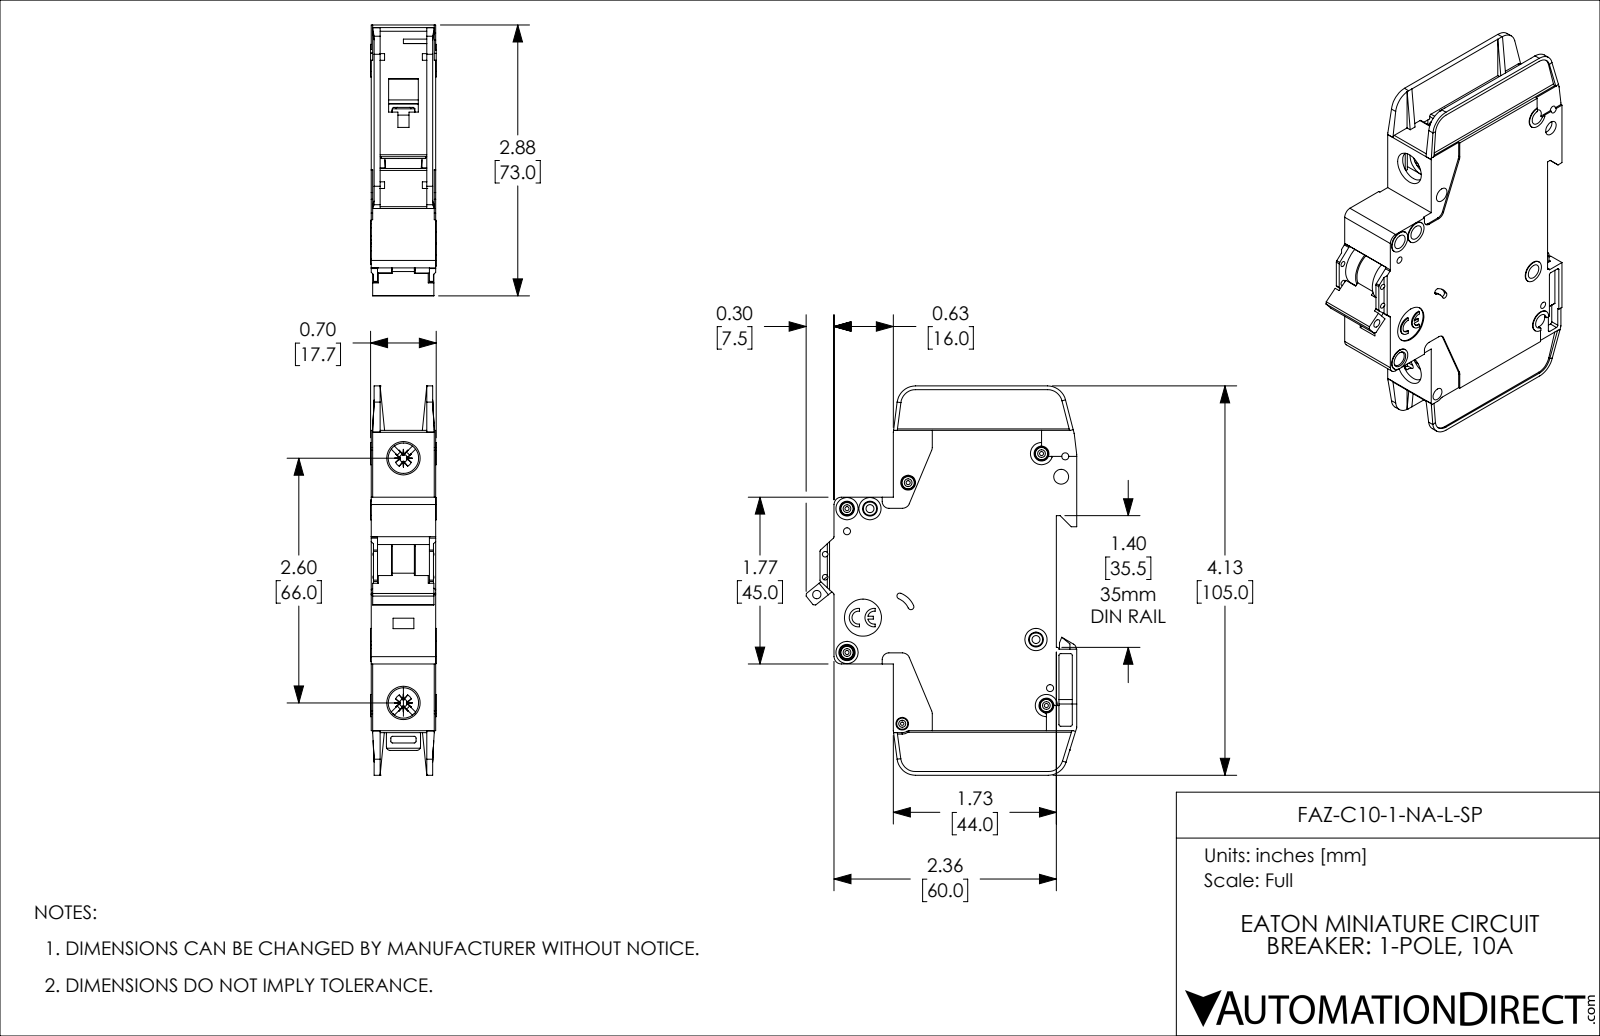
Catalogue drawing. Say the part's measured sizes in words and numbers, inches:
The part is named "FAZ-C10-1-NA-L-SP". Its 3-D file was written by "SolidWorks 2019 (AUTOMOTIVE_DESIGN)". It is 1 solid with 1127 faces: 671 planar, 357 cylindrical and 99 other. Overall it measures 4.134 by 2.876 by 0.697 inches. Its volume is 4.682 cubic inches and its surface area 41.01 square inches. Round holes: 8 of diameter 0.157, 5 of diameter 0.043, 4 of diameter 0.075, 2 of diameter 0.059, 2 of diameter 0.085, 2 of diameter 0.323, 1 of diameter 0.035, 1 of diameter 0.089, 1 of diameter 0.098, 1 of diameter 0.134, 1 of diameter 0.394. Round bosses or shafts: 5 of diameter 0.13, 4 of diameter 0.236, 2 of diameter 0.118, 1 of diameter 0.098. Partial cylindrical surfaces (rounded edges, fillets, slot ends): 42 of radius 0.02, 10 of radius 0.016, 10 of radius 0.039, 8 of radius 0.079, 5 of radius 0.197, 4 of radius 0.008, 4 of radius 0.026, 4 of radius 0.043. The main face-to-face distances are 0.047, 0.685, 0.591, 0.638, 0.094, 0.543, 0.016, 0.031, 0.496, 0.575. The hole center spacings are 0.244, 0.537, 0.87, 0.189, 0.199, 0.204, 0.221, 0.24.
